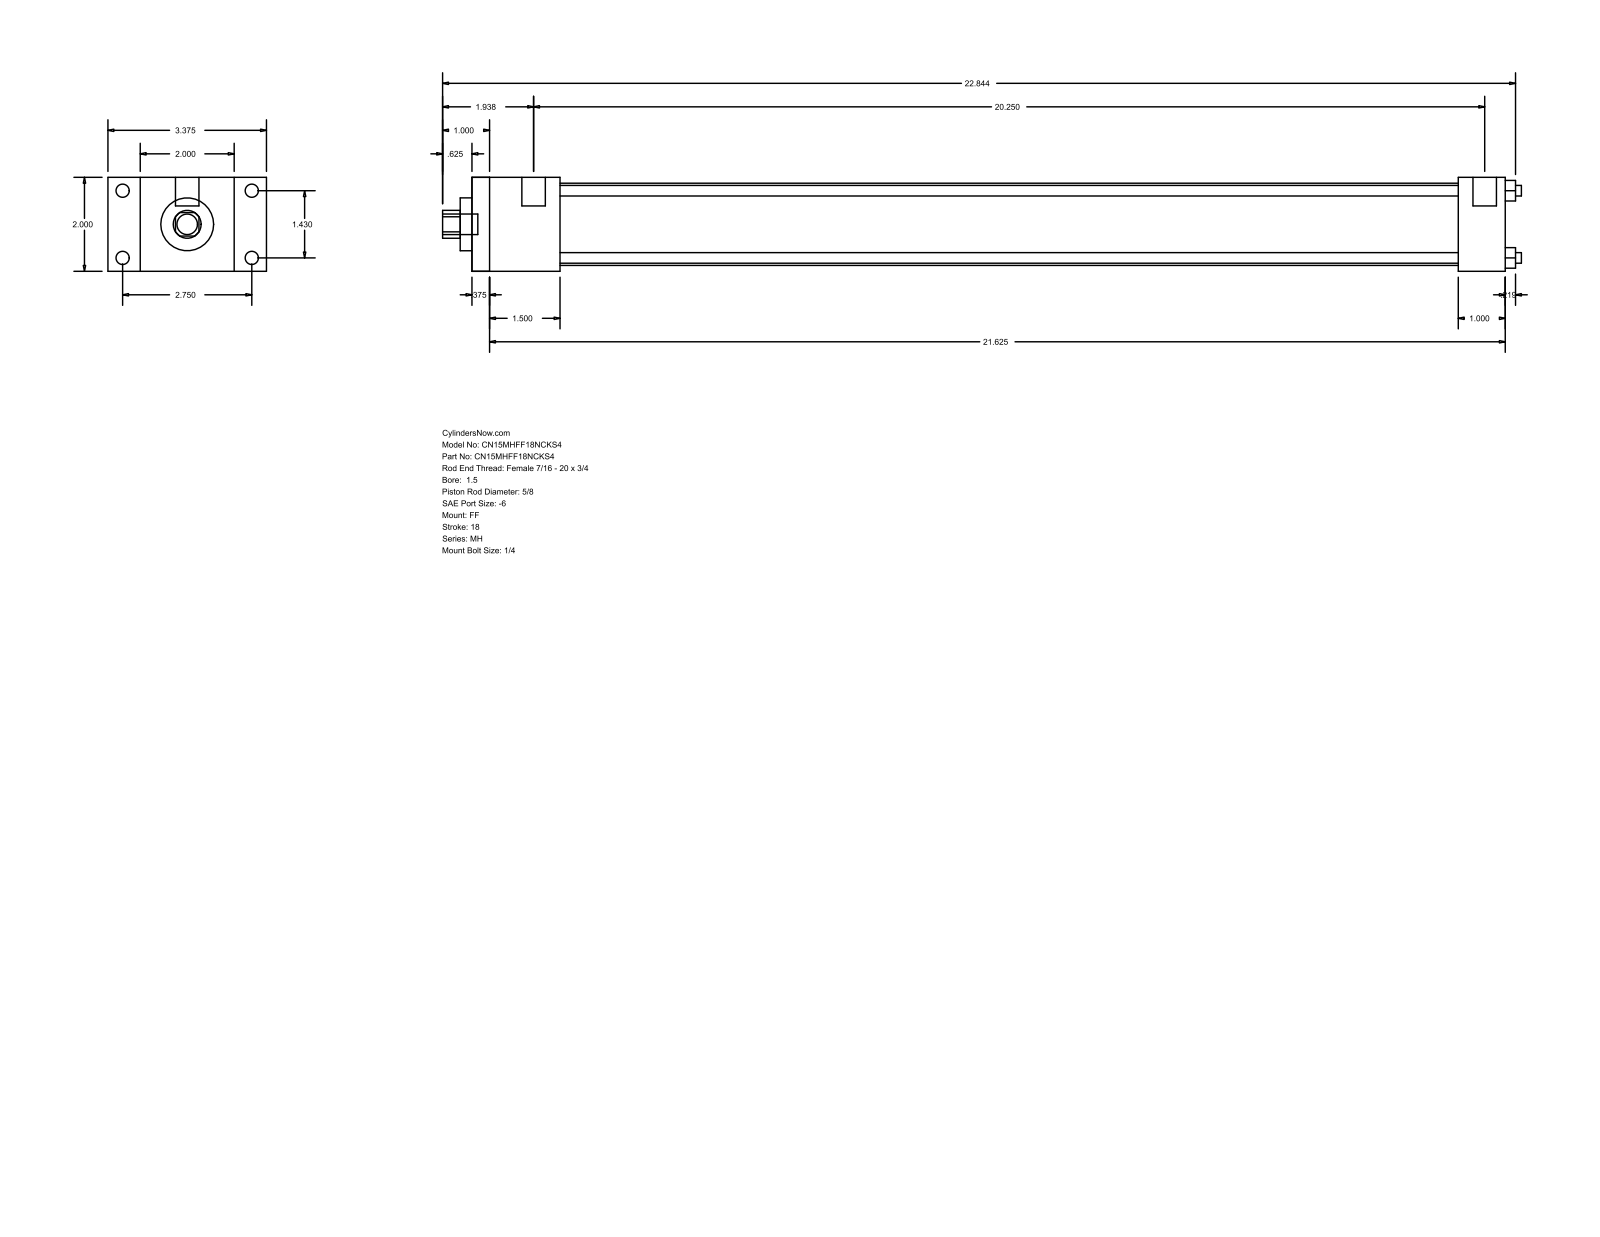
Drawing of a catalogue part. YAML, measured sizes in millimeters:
part_name: "MH_FF__0150_0.625"
step_written_by: "GSSL Pune (CONFIG_CONTROL_DESIGN)"
units: millimeters
bodies: {solids: 0, faces: 92, planar: 64, cylindrical: 28, other: 0}
overall_size: [583.41, 85.72, 50.8]
round_holes:
  - {diameter: 5.71, count: 4}
  - {diameter: 15.88, count: 1}
  - {diameter: 28.57, count: 1}
  - {diameter: 44.45, count: 1}
round_bosses_or_shafts:
  - {diameter: 7.14, count: 4}
  - {diameter: 5.56, count: 4}
  - {diameter: 12.7, count: 2}
  - {diameter: 11.11, count: 1}
partial_cylinders:
  - {radius: 7.54, count: 1}
face_to_face_distances: [50.8, 558.79, 9.52, 549.27, 25.4, 17.46, 68.26, 47.62, 38.1, 511.17]
hole_center_spacings: [25.68, 36.32, 51.36]
